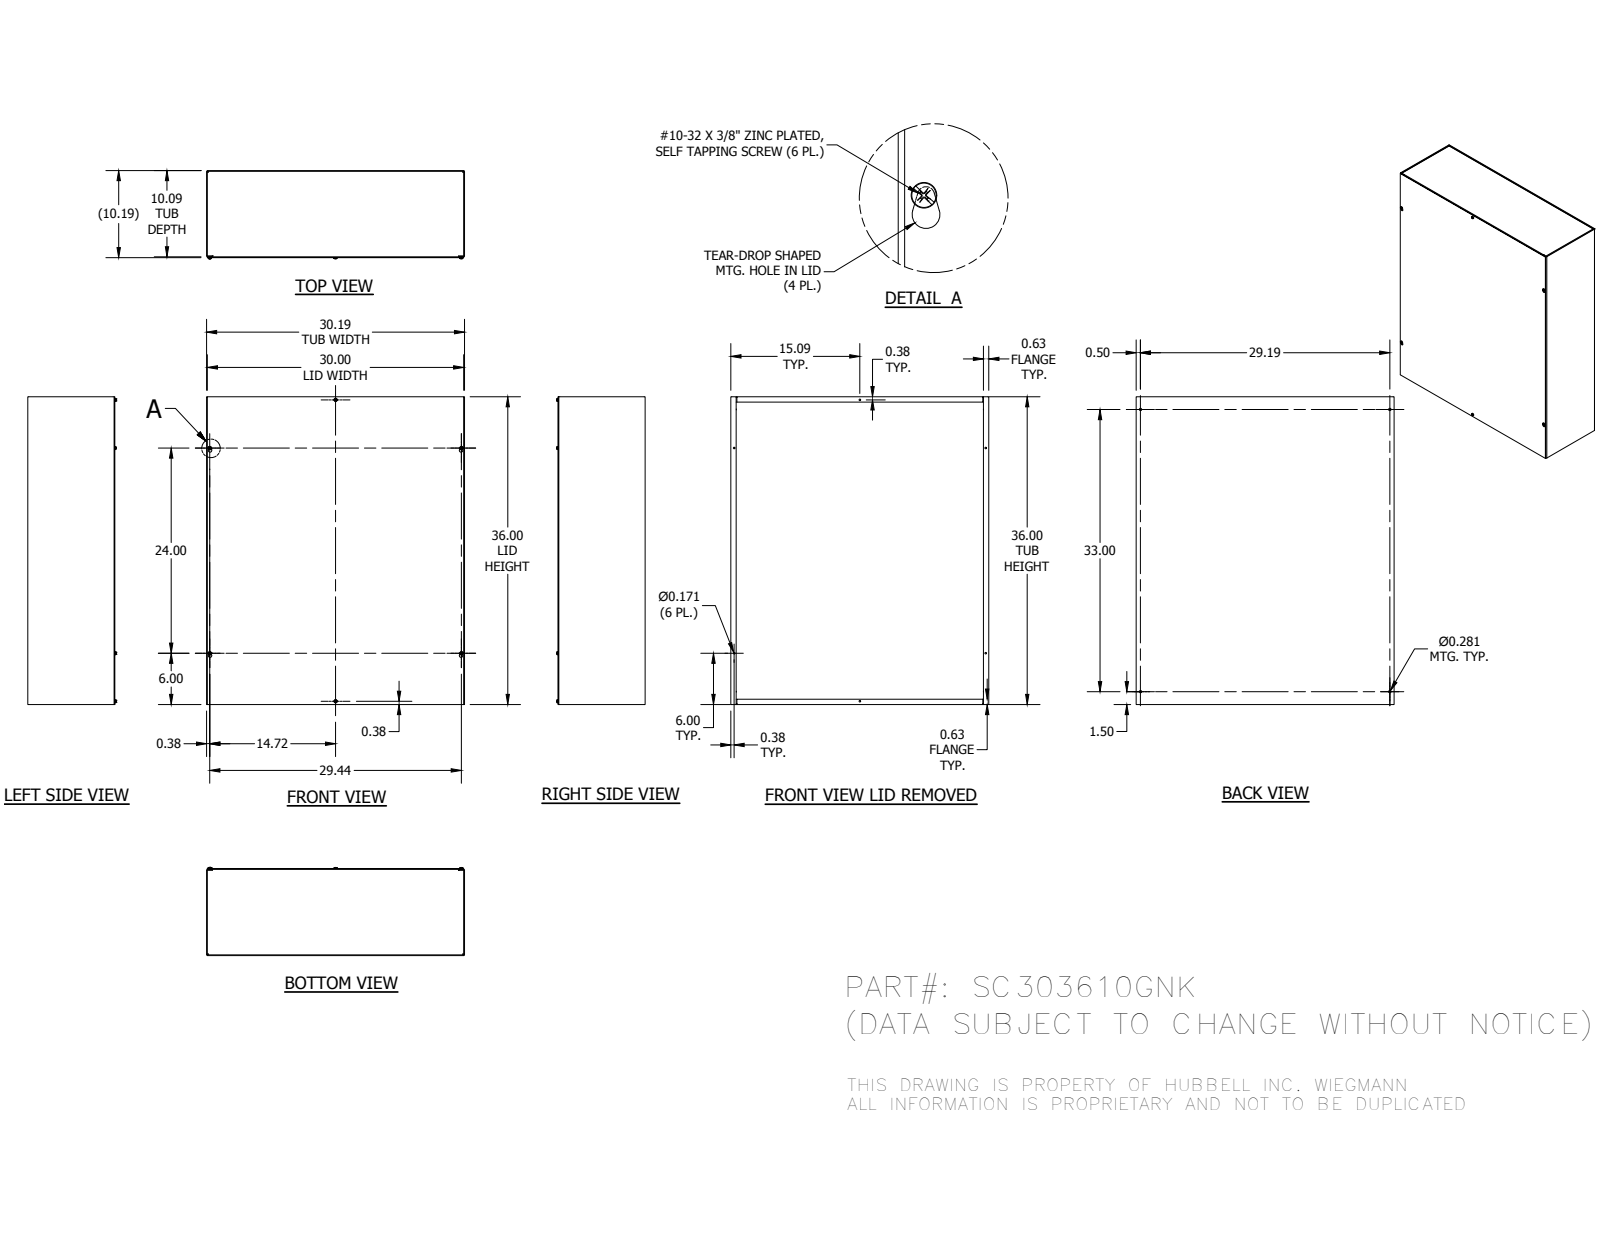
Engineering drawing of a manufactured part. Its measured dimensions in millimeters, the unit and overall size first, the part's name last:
Units: millimetres
Overall size (bounding box): 914.4 × 766.76 × 262.11
Round holes (diameter × count): ⌀4.34 ×6, ⌀7.14 ×4, ⌀7.92 ×2
Round bosses / shafts (diameter × count): ⌀4.83 ×6
Partial cylindrical surfaces — rounded edges, fillets, slot ends (radius × count): R0.4 ×12, R2.78 ×12, R3.17 ×4, R5.16 ×4
Main face-to-face distances: 2.38, 256.38, 254, 258.76, 764.38, 912.02, 762, 766.76, 914.4, 909.64
Hole centre spacings: 371.78, 400.23, 942.71, 114.34, 723.91, 753.26, 840.23, 1038.45
Volume: 5 530 000 mm³ · Surface area: 4 675 000 mm²
Bodies: 10 solids, 404 faces (232 planar, 50 cylindrical, 122 other)
Part name (STEP PRODUCT): SC303610GNKBLR; SC3010GNKTB; SC3036GLPA; 37214 (+1 more)
STEP written by: Autodesk Inventor 2014 (AUTOMOTIVE_DESIGN)
